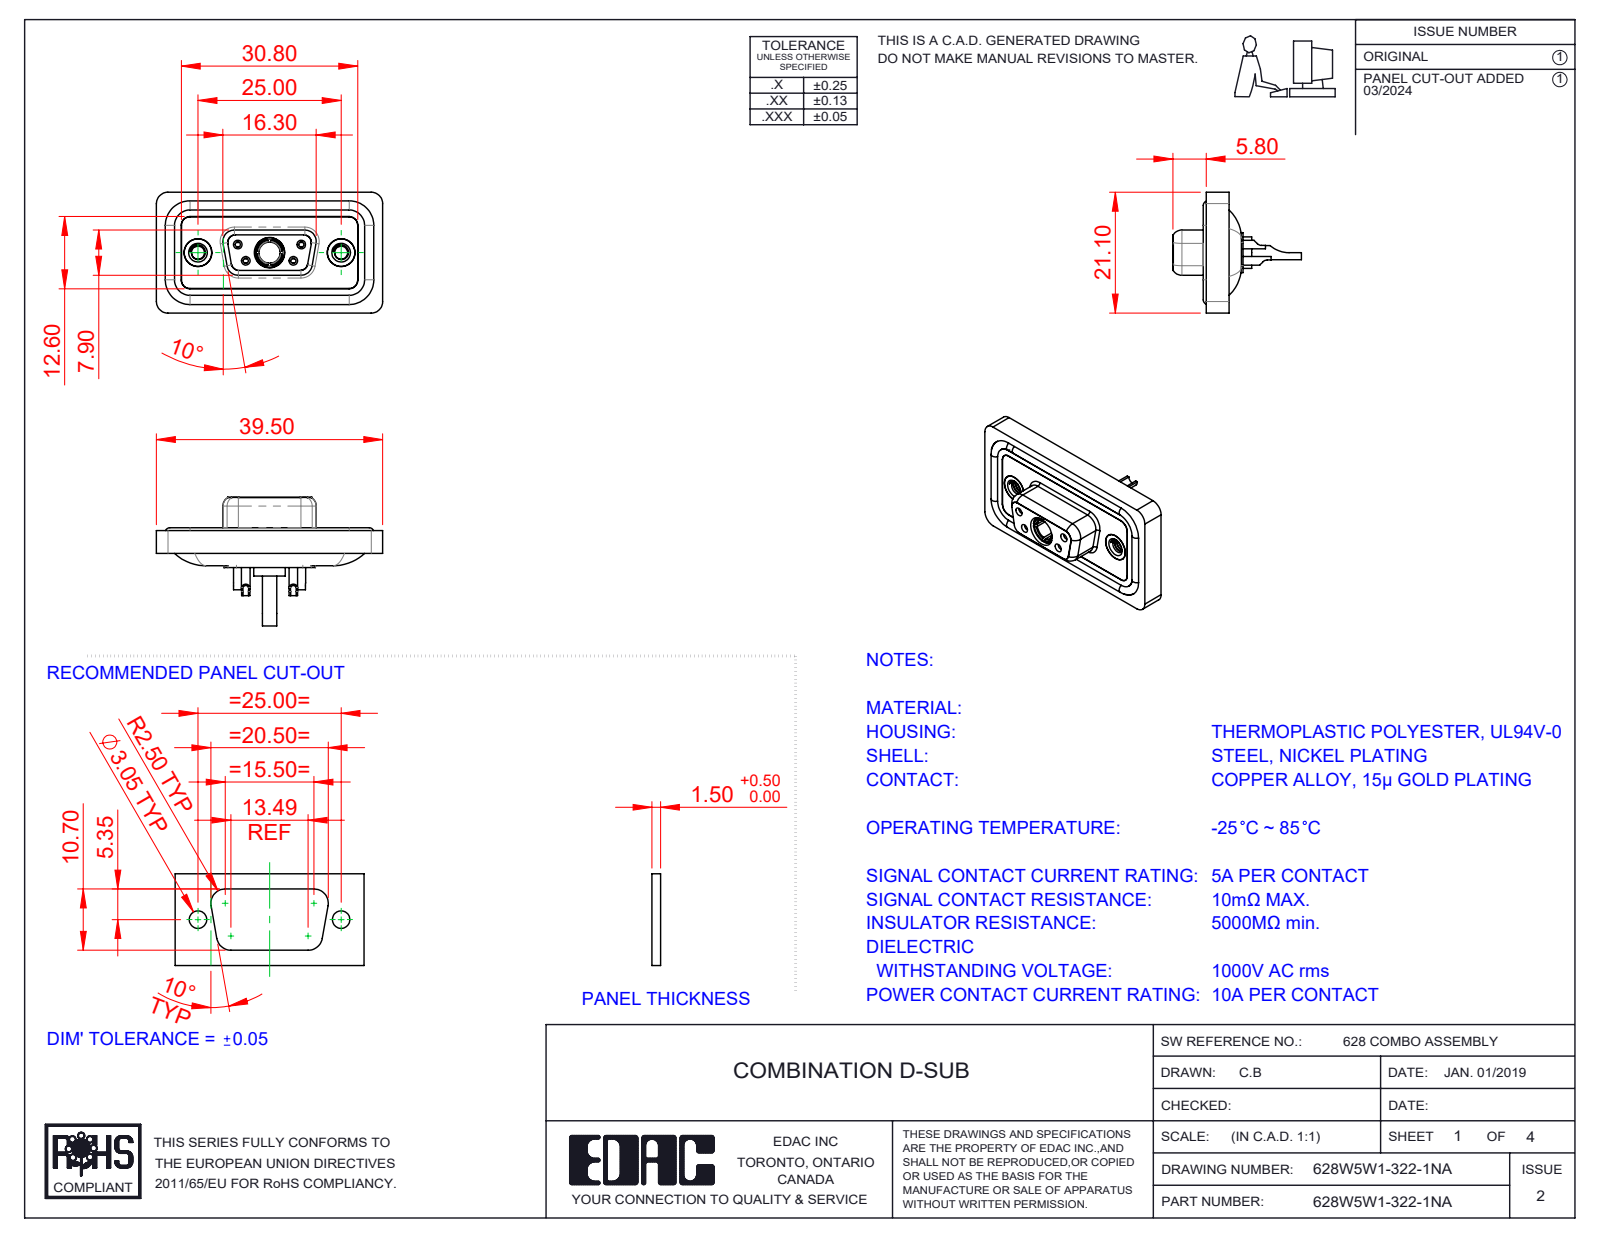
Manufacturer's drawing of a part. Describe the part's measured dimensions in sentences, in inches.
The part is named "628Combo Waterproof Housing_09 Contacts; 628Combo Housing_5W1; 628W5W1-322-1NA; Power Socket_10A SC (+5 more)". Its 3-D file was written by "SolidWorks 2023 (CONFIG_CONTROL_DESIGN)". It is 13 solids with 683 faces: 204 planar, 300 cylindrical and 179 other. Overall it measures 1.555 by 0.884 by 0.831 inches. Its volume is 0.291 cubic inches and its surface area 11.97 square inches. Round holes: 4 of diameter 0.035, 4 of diameter 0.039, 4 of diameter 0.043, 4 of diameter 0.059, 4 of diameter 0.079, 3 of diameter 0.191, 2 of diameter 0.063, 2 of diameter 0.067, 2 of diameter 0.089, 2 of diameter 0.157, 2 of diameter 0.159, 2 of diameter 0.197. Round bosses or shafts: 6 of diameter 0.063, 4 of diameter 0.087, 2 of diameter 0.195, 2 of diameter 0.189, 1 of diameter 0.217, 1 of diameter 0.205, 1 of diameter 0.195, 1 of diameter 0.187. Partial cylindrical surfaces (rounded edges, fillets, slot ends): 22 of radius 0.059, 18 of radius 0.079, 8 of radius 0.053, 8 of radius 0.063, 6 of radius 0.039, 4 of radius 0.01, 4 of radius 0.02, 4 of radius 0.024. The main face-to-face distances are 0.016, 0.114, 0.071, 0.043, 0.063, 0.02, 0.222, 0.293, 0.211, 0.142. The hole center spacings are 0.124, 0.225, 0.28, 0.492, 0.713, 0.173, 0.173, 0.327.
